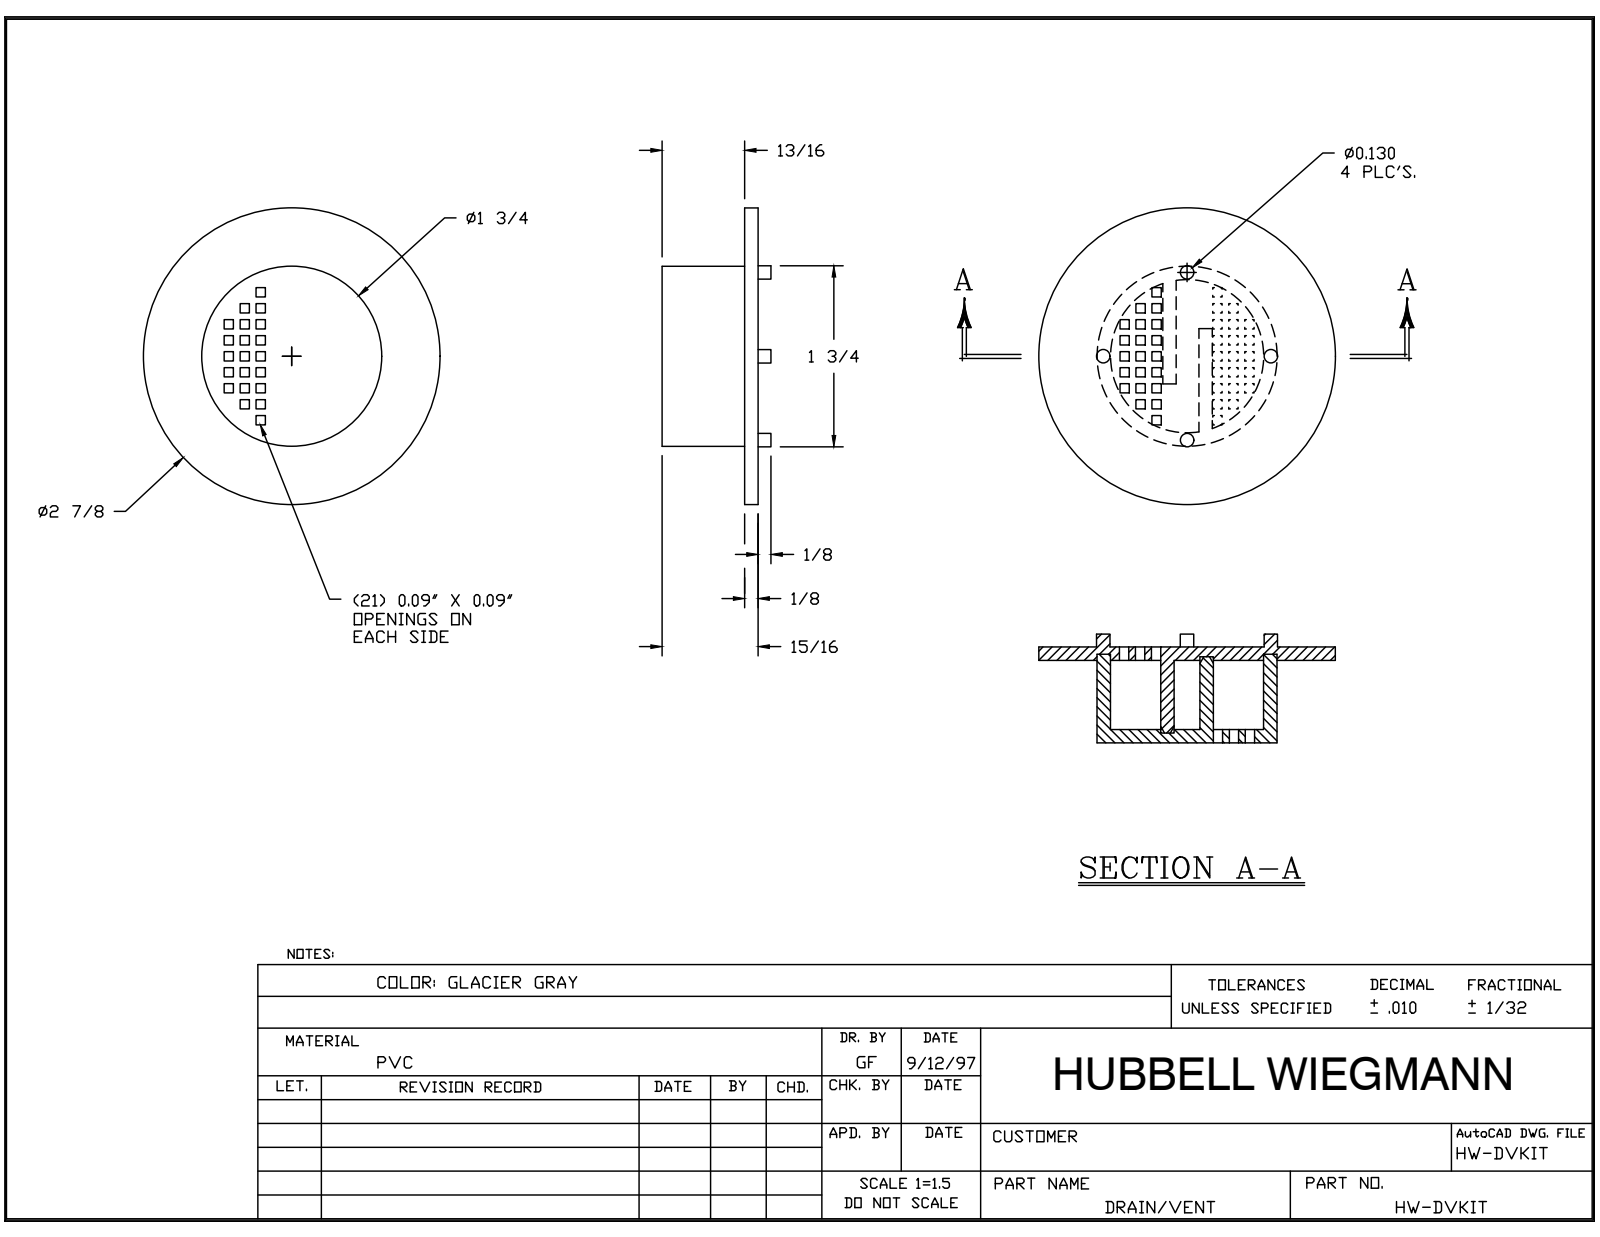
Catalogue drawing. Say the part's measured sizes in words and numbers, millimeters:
The part is named "PARTA; PARTB; DVK3KIT_STP". Its 3-D file was written by "Autodesk Inventor 2014 (AUTOMOTIVE_DESIGN)". It is 2 solids with 199 faces: 190 planar, 9 cylindrical and 0 other. Overall it measures 57.15 by 57.15 by 25.4 millimeters. Its volume is 21 697 cubic millimeters and its surface area 16 751 square millimeters. Round holes: 1 of diameter 38.1, 1 of diameter 44.45. Round bosses or shafts: 4 of diameter 3.17, 1 of diameter 57.15. The main face-to-face distances are 3.17, 19.05, 22.22, 15.88, 17.46, 1.59, 1.58, 3.18, 20.63, 0.79.
